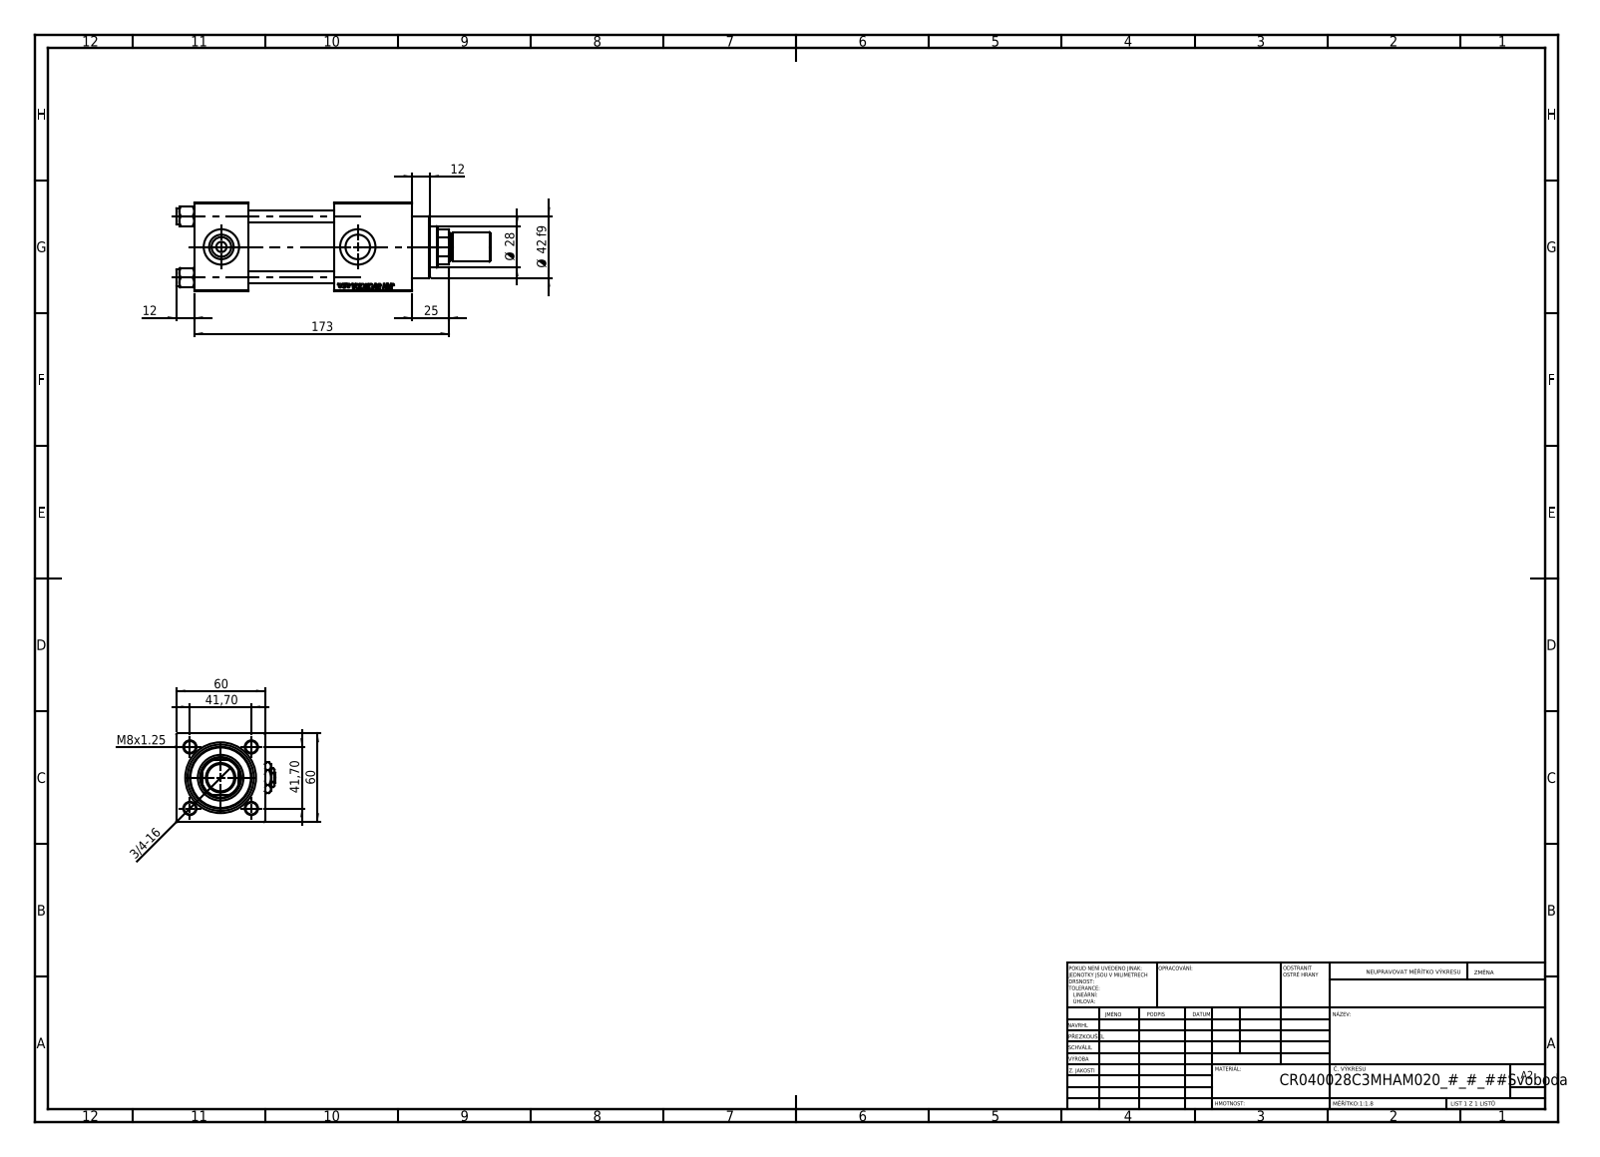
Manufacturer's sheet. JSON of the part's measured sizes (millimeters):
{"part_name": "NUT_M5_C; V215CR_C_Body; V215_VC_A; ROD_END_AH (+3 more)", "step_written_by": "SolidWorks 2019 (CONFIG_CONTROL_DESIGN)", "units": "millimeters", "bodies": {"solids": 14, "faces": 1264, "planar": 578, "cylindrical": 102, "other": 584}, "overall_size": [213, 67, 60], "volume_mm3": 429590, "surface_area_mm2": 116784, "round_holes": [[8, 4], [7, 2], [16.66, 2], [24, 2], [18.5, 1], [28, 1], [31, 1], [40, 1], [45, 1]], "round_bosses_or_shafts": [[11, 4], [46, 1], [42, 1], [20, 1], [18, 1]], "partial_cylinders_radius": [[13.5, 1]], "face_to_face_distances": [60, 37, 58, 53, 95, 119.3, 82.3, 24.3, 148, 111], "hole_center_spacings": [29.49, 41.7, 58.97, 92.5]}
